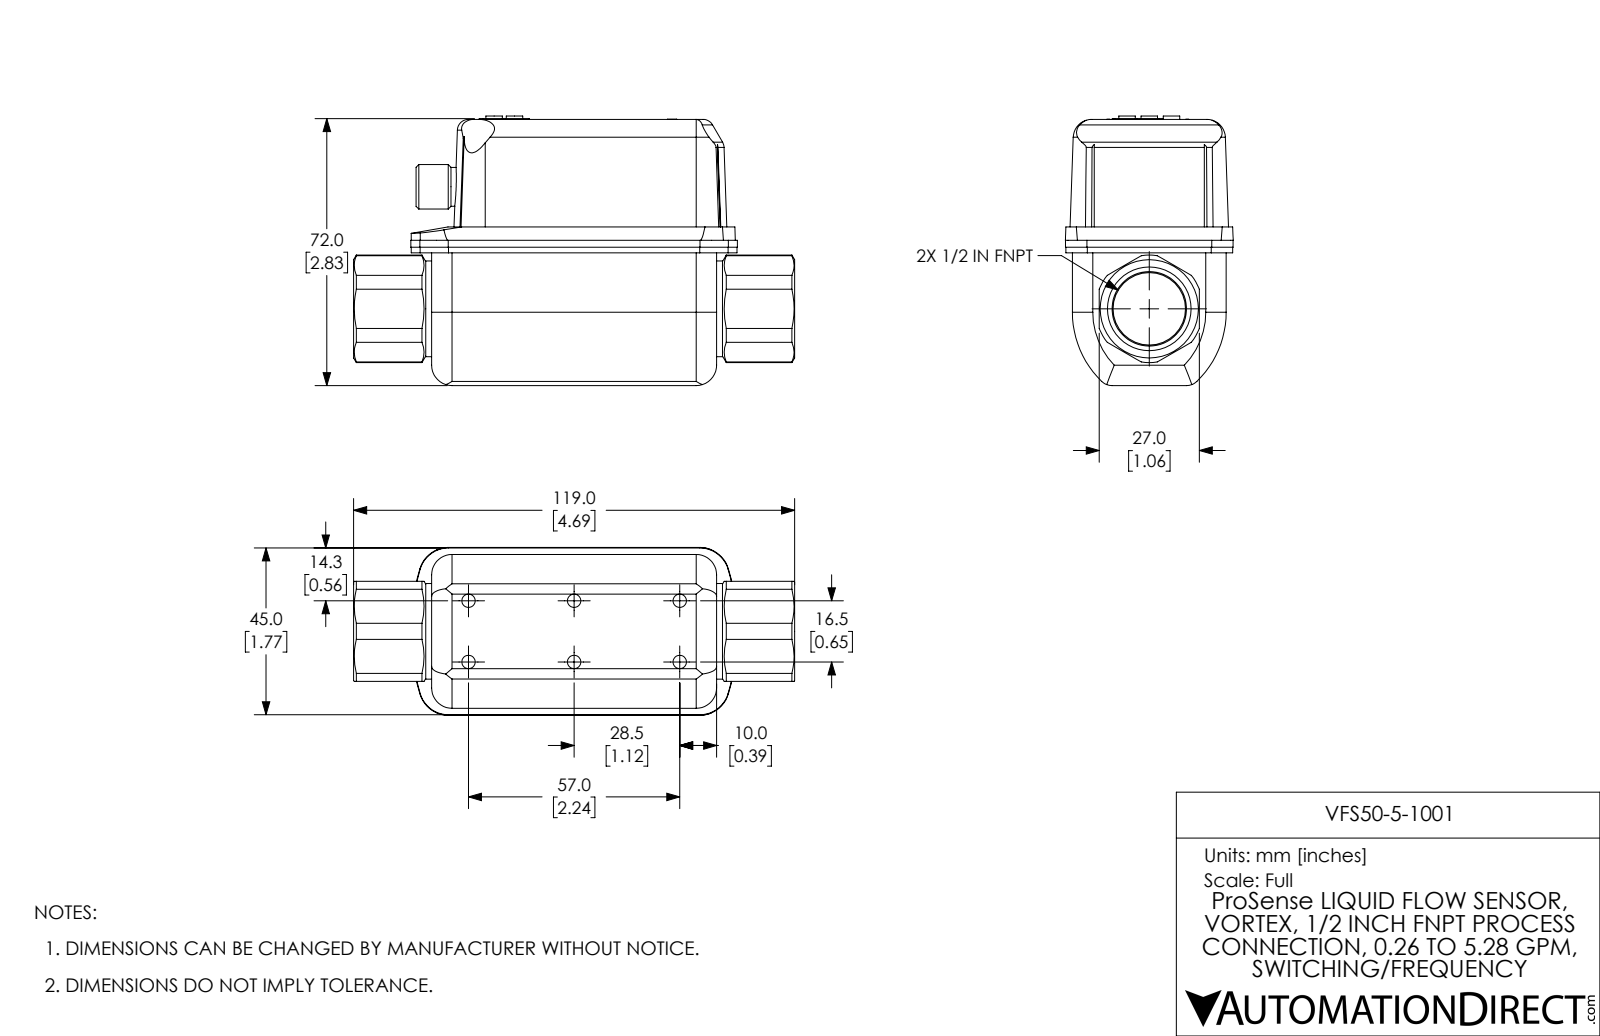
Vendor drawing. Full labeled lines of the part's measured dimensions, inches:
Part name (STEP PRODUCT): VFS50-5-1001
STEP written by: SolidWorks 2017 (AUTOMOTIVE_DESIGN)
Units: inches
Bodies: 1 solid, 219 faces (84 planar, 80 cylindrical, 55 other)
Overall size (bounding box): 4.685 × 2.862 × 1.783
Volume: 14.29 in³ · Surface area: 42.78 in²
Round holes (diameter × count): ⌀0.142 ×6, ⌀0.331 ×1
Round bosses / shafts (diameter × count): ⌀0.175 ×3, ⌀1.016 ×1, ⌀0.472 ×1, ⌀0.413 ×1
Partial cylindrical surfaces — rounded edges, fillets, slot ends (radius × count): R0.315 ×12, R0.217 ×6, R0.157 ×4, R2.362 ×4, R0.138 ×2, R0.197 ×2, R1.024 ×2, R0.024 ×1
Main face-to-face distances: 1.063, 2.827, 1.634, 1.417, 0.285, 1.348, 2.825, 1.409, 1.415, 0.435
Hole centre spacings: 1.122, 1.296, 0.65, 2.244, 2.336
